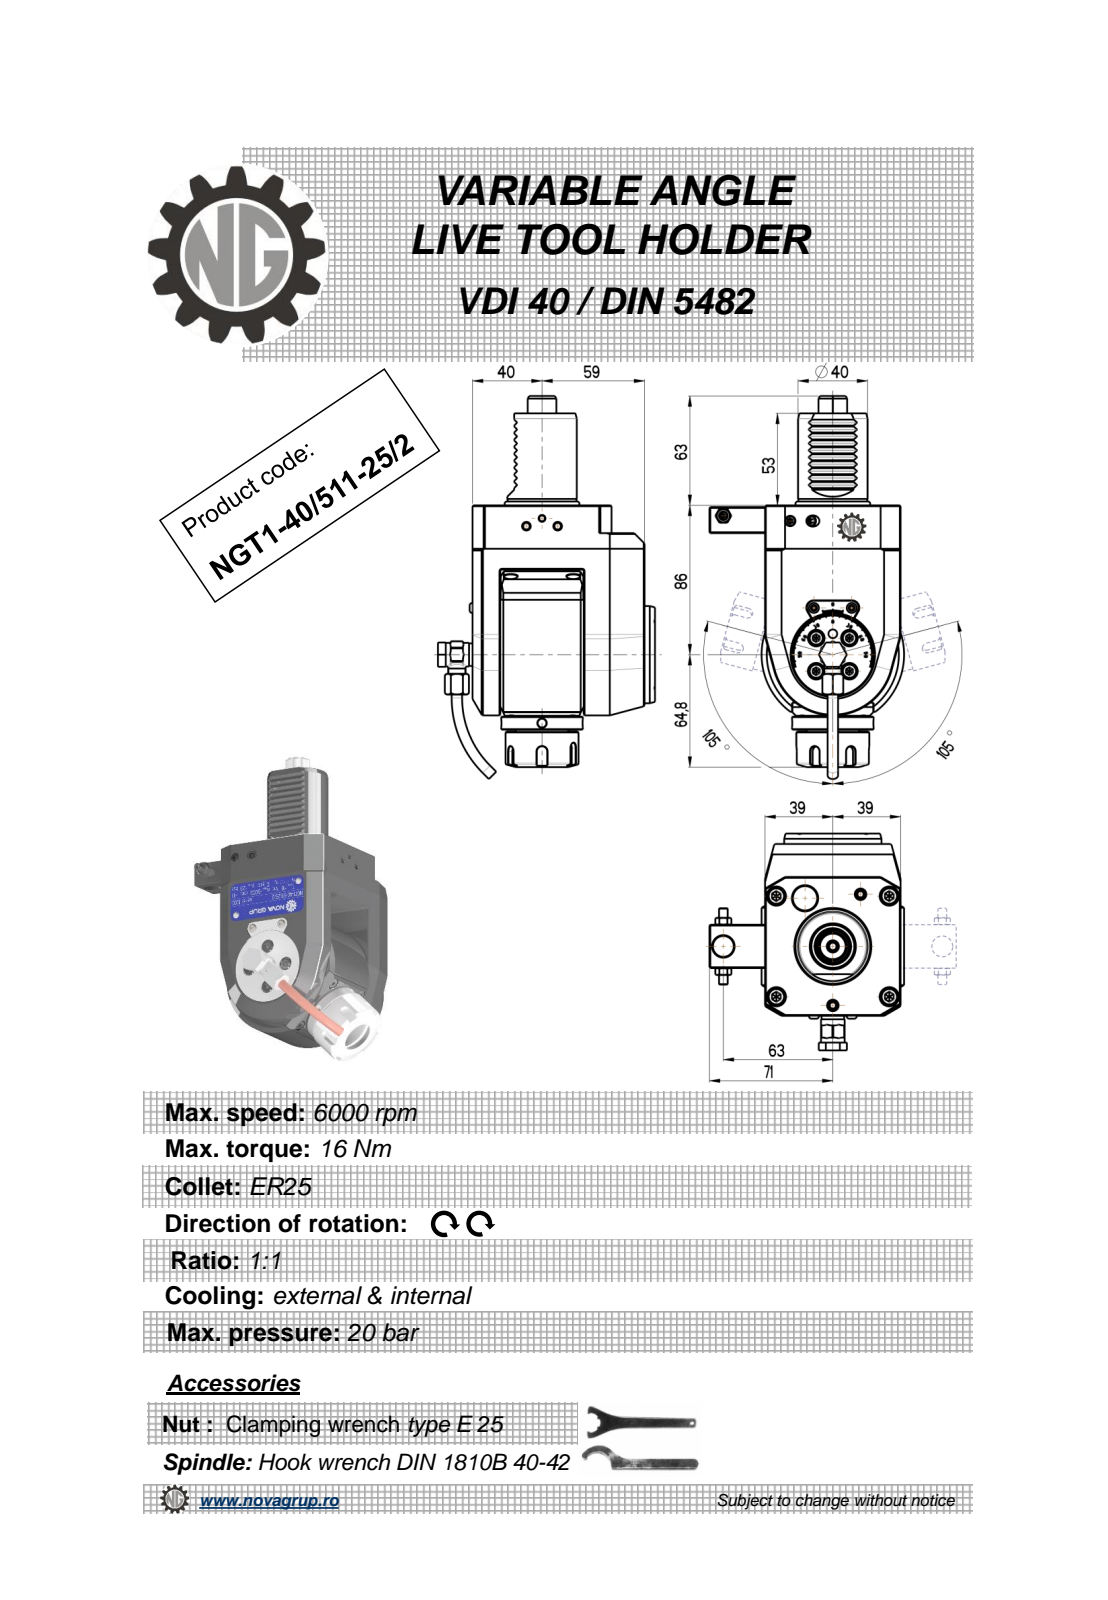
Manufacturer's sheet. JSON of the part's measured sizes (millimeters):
{"part_name": "NGT1_40_511_25_2", "step_written_by": "PRO/ENGINEER BY PARAMETRIC TECHNOLOGY CORPORATION, 2010280 (CONFIG_CONTROL_DESIGN)", "units": "millimeters", "bodies": {"solids": 1, "faces": 621, "planar": 244, "cylindrical": 179, "other": 198}, "overall_size": [220.67, 124.9, 112], "volume_mm3": 920612, "surface_area_mm2": 82365, "round_holes": [[4, 5], [4.2, 2], [3, 1], [6.2, 1], [9, 1], [9.5, 1], [11, 1], [12, 1], [20.3, 1]], "round_bosses_or_shafts": [[10, 2], [6, 2], [5.7, 2], [56, 1], [42, 1], [40, 1], [32.99, 1], [13.6, 1]], "partial_cylinders_radius": [[3.03, 18], [0.26, 12], [0.3, 10], [0.16, 6], [3, 5], [0.5, 4], [1, 2], [10, 2]], "face_to_face_distances": [16, 37, 99, 78, 64, 6, 105, 21, 1, 89], "hole_center_spacings": [0.4, 38.95, 49, 49.4, 63, 79.81, 80.06, 101.83]}
